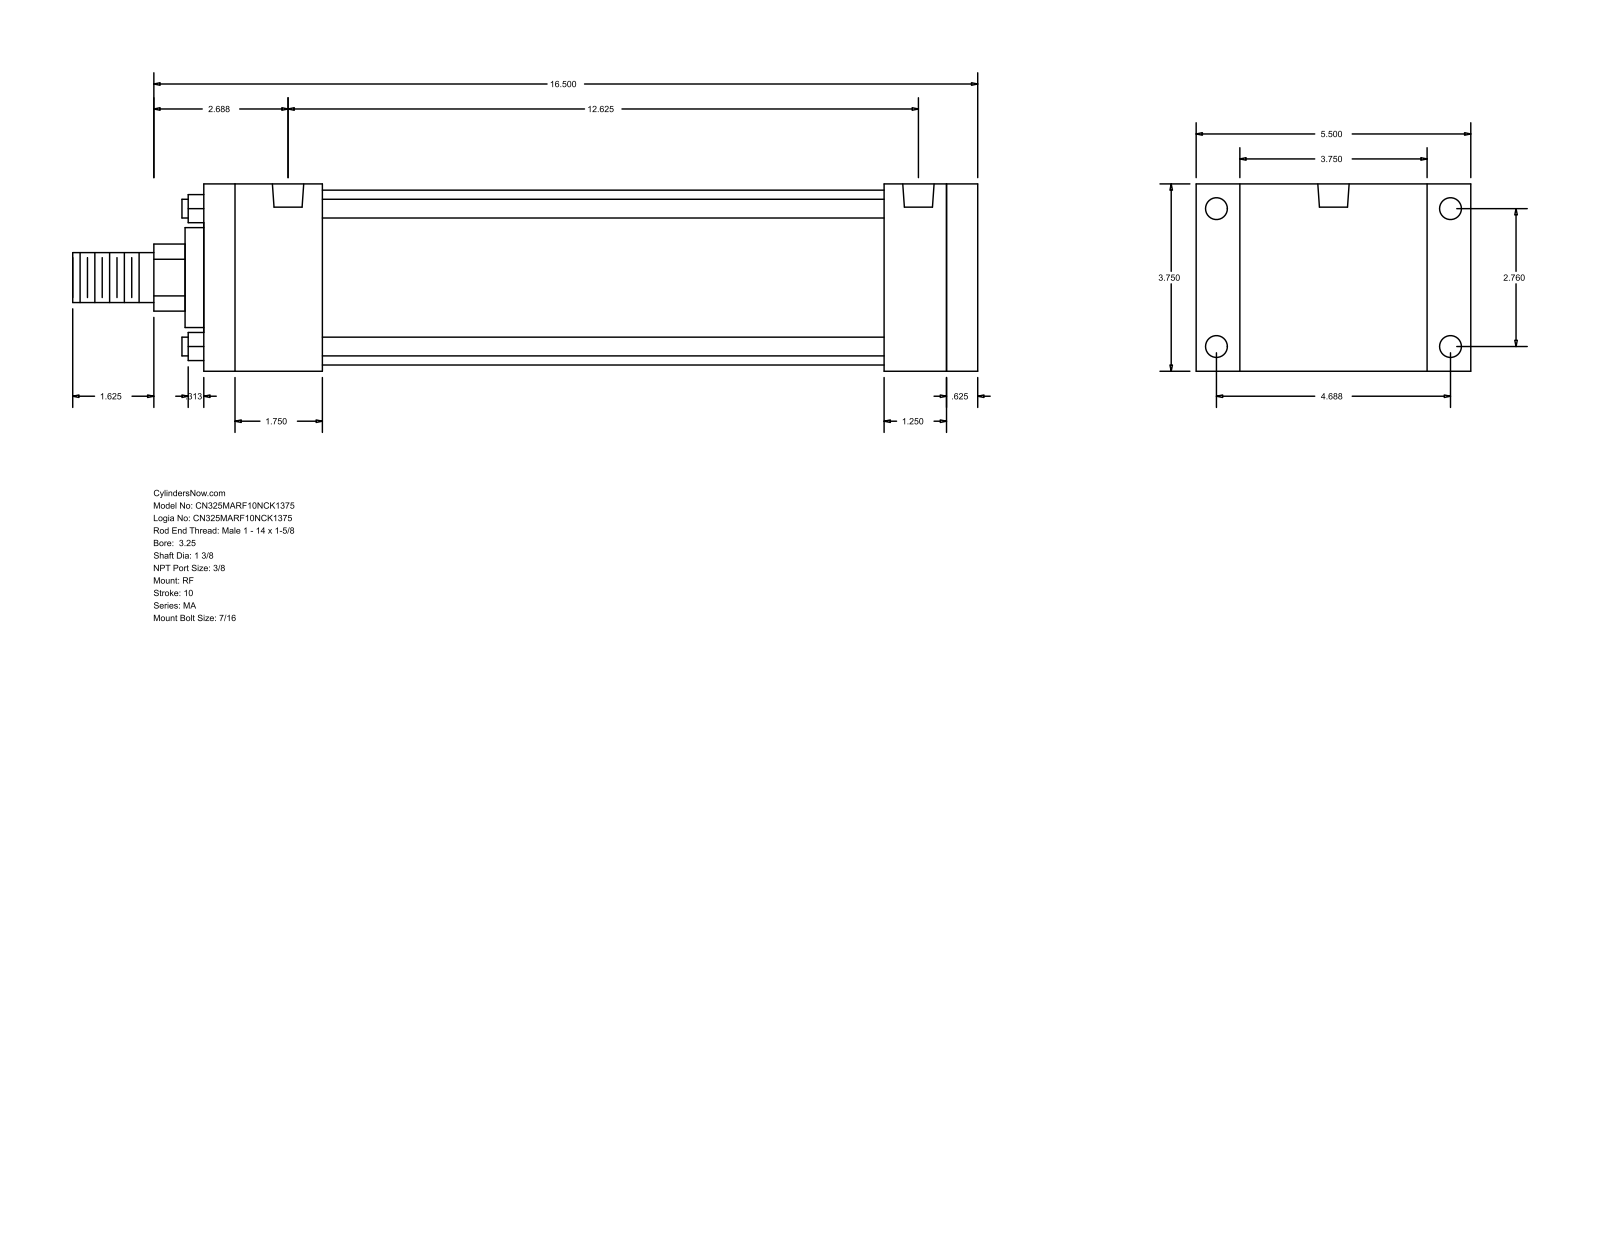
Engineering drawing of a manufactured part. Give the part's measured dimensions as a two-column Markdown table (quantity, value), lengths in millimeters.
| quantity | value |
| --- | --- |
| part name | MA_RF__0325_1.375 |
| STEP written by | GSSL Pune (CONFIG_CONTROL_DESIGN) |
| units | millimeters |
| bodies | 0 solids, 92 faces (64 planar, 28 cylindrical, 0 other) |
| overall size | 460.38 × 139.7 × 95.25 |
| round holes (diameter × count) | 11.11 × 8, 15.93 × 2 |
| round bosses / shafts (diameter × count) | 9.53 × 4, 88.9 × 1, 50.8 × 1, 34.92 × 1, 25.4 × 1 |
| partial cylindrical surfaces (radius × count) | 17.06 × 1 |
| main face-to-face distances | 95.24, 393.7, 377.83, 15.87, 22.23, 117.47, 346.08, 31.75, 47.62, 60.32 |
| hole center spacings | 70.1, 119.06, 138.16, 311.15, 4.76, 4.77, 315.91, 315.92 |
